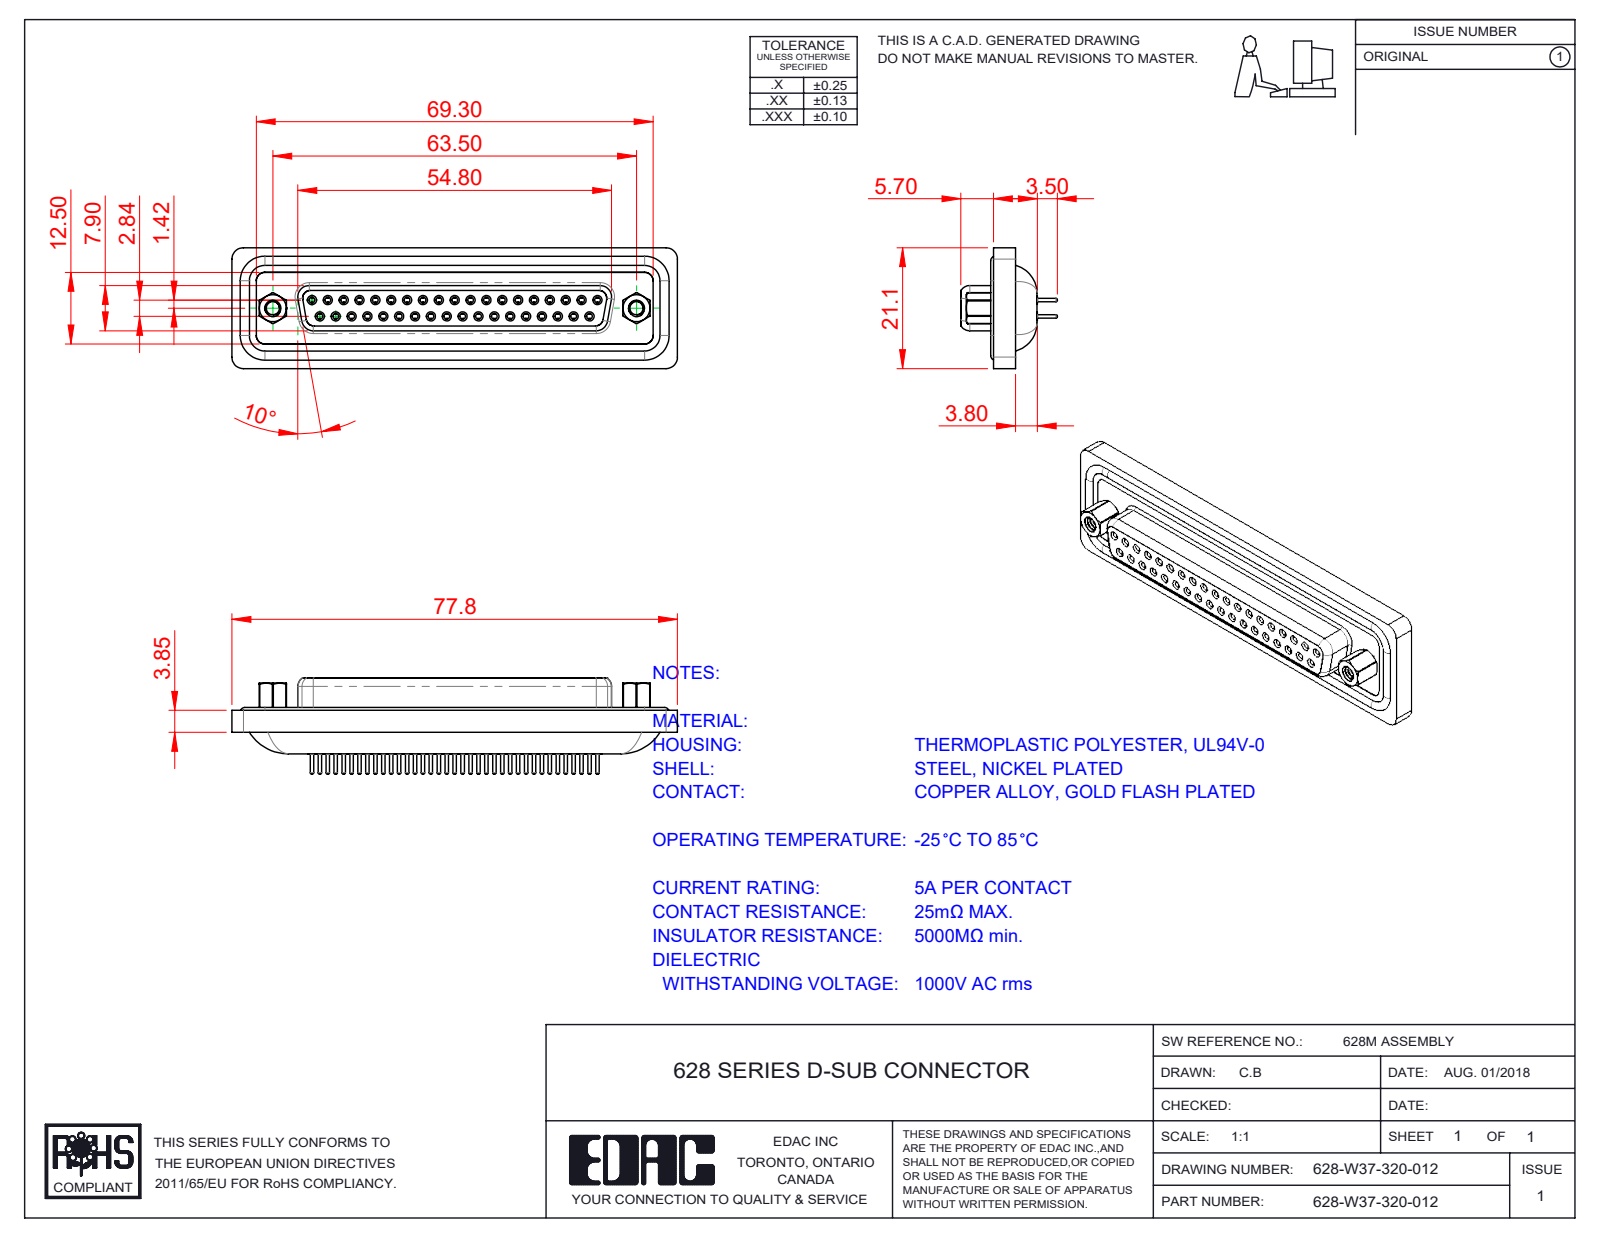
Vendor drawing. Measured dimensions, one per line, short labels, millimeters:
name: 628W Contact Row 2_20; 628W Shell Front_37 Contacts; 628-W37-320-012; 628W 4-40 Threaded Rivet (+4 more)
written by: SolidWorks 2020 (CONFIG_CONTROL_DESIGN)
unit: mm
bodies: 45 solids, 2532 faces (656 planar, 997 cylindrical, 879 other)
size: 77.8 × 21.1 × 16.85
volume: 11 040 mm³; area: 17 776 mm²
holes: 37× ⌀1, 37× ⌀1.1, 37× ⌀1.5, 37× ⌀1.7, 37× ⌀1.8, 37× ⌀2, 2× ⌀2.26, 2× ⌀2.29, 2× ⌀4, 2× ⌀4.8, 2× ⌀5
bosses: 41× ⌀1.6, 37× ⌀2.2, 37× ⌀0.6, 8× ⌀1.5, 2× ⌀4.9, 2× ⌀2.79
rounds: 16× R2, 14× R1.5, 8× R1.35, 6× R2.7, 4× R0.5, 4× R0.9, 4× R1.6, 4× R1.75
face distances: 0.4, 7.45, 7.5, 8.45, 6.2, 13.65, 3.75, 4.1, 1.1, 2.75
hole spacings: 3.16, 2.77, 5.54, 8.31, 5.04, 7.49, 11.08, 13.85
